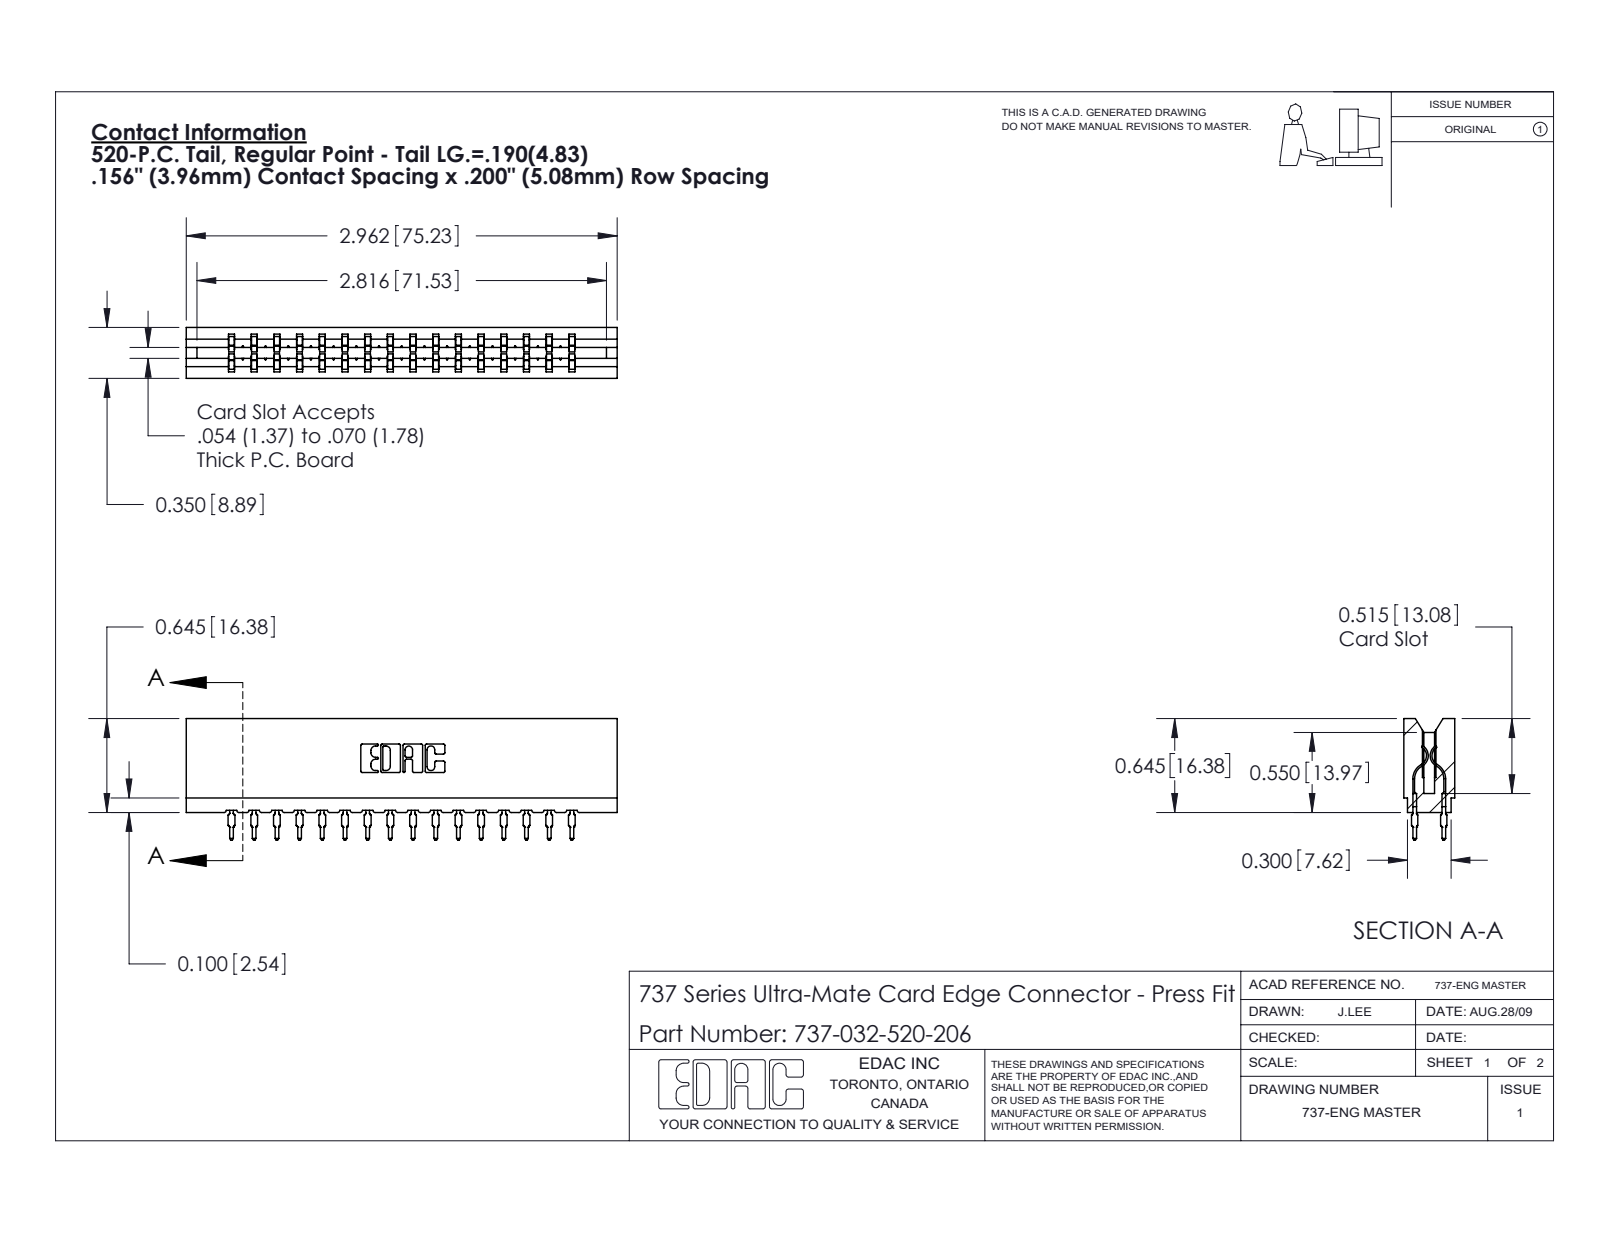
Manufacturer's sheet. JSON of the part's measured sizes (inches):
{"part_name": "737-032-520-206; 745-292-001_520; 737 Part_Insulator Option - 06", "step_written_by": "SolidWorks 2020 (CONFIG_CONTROL_DESIGN)", "units": "inches", "bodies": {"solids": 33, "faces": 2975, "planar": 1543, "cylindrical": 600, "other": 832}, "overall_size": [2.962, 0.836, 0.35], "volume_in3": 0.461, "surface_area_in2": 15.87, "partial_cylinders_radius": [[0.021, 64], [0.015, 32], [0.01, 22], [0.005, 8], [0.011, 8], [0.007, 6], [0.031, 6], [0.026, 3]], "face_to_face_distances": [0.138, 0.212, 0.35, 0.156, 0.624, 0.78, 0.468, 0.312, 0.074, 0.936]}
